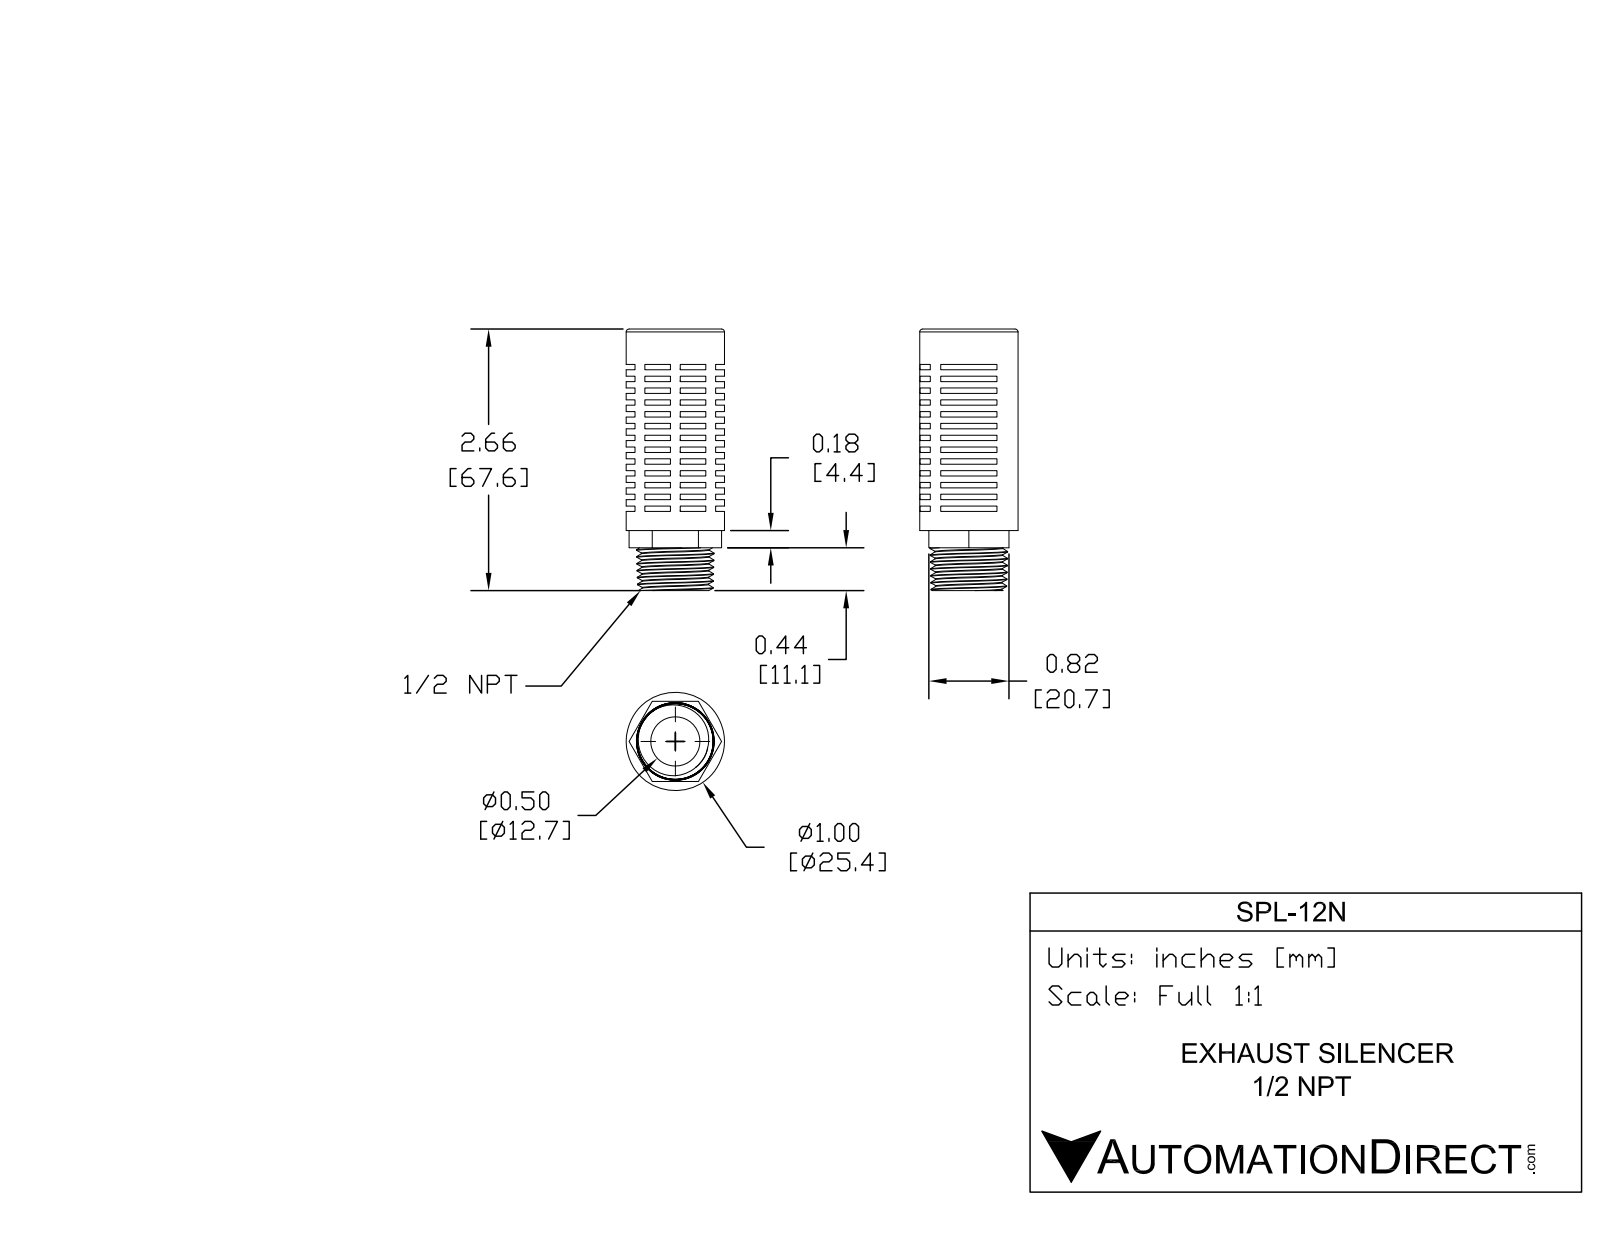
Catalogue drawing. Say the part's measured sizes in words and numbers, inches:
The part is named "SPL-12N". Its 3-D file was written by "SolidWorks 2015 (CONFIG_CONTROL_DESIGN)". It is 1 solid with 270 faces: 246 planar, 4 cylindrical and 20 other. Overall it measures 2.66 by 1 by 1 inches. Its volume is 1.127 cubic inches and its surface area 24.58 square inches. Round holes: 1 of diameter 0.5. Round bosses or shafts: 1 of diameter 1. The main face-to-face distances are 0.12, 0.36, 0.24, 0.6, 0.48, 0.415, 0.72, 0.36, 1.015, 0.535.
